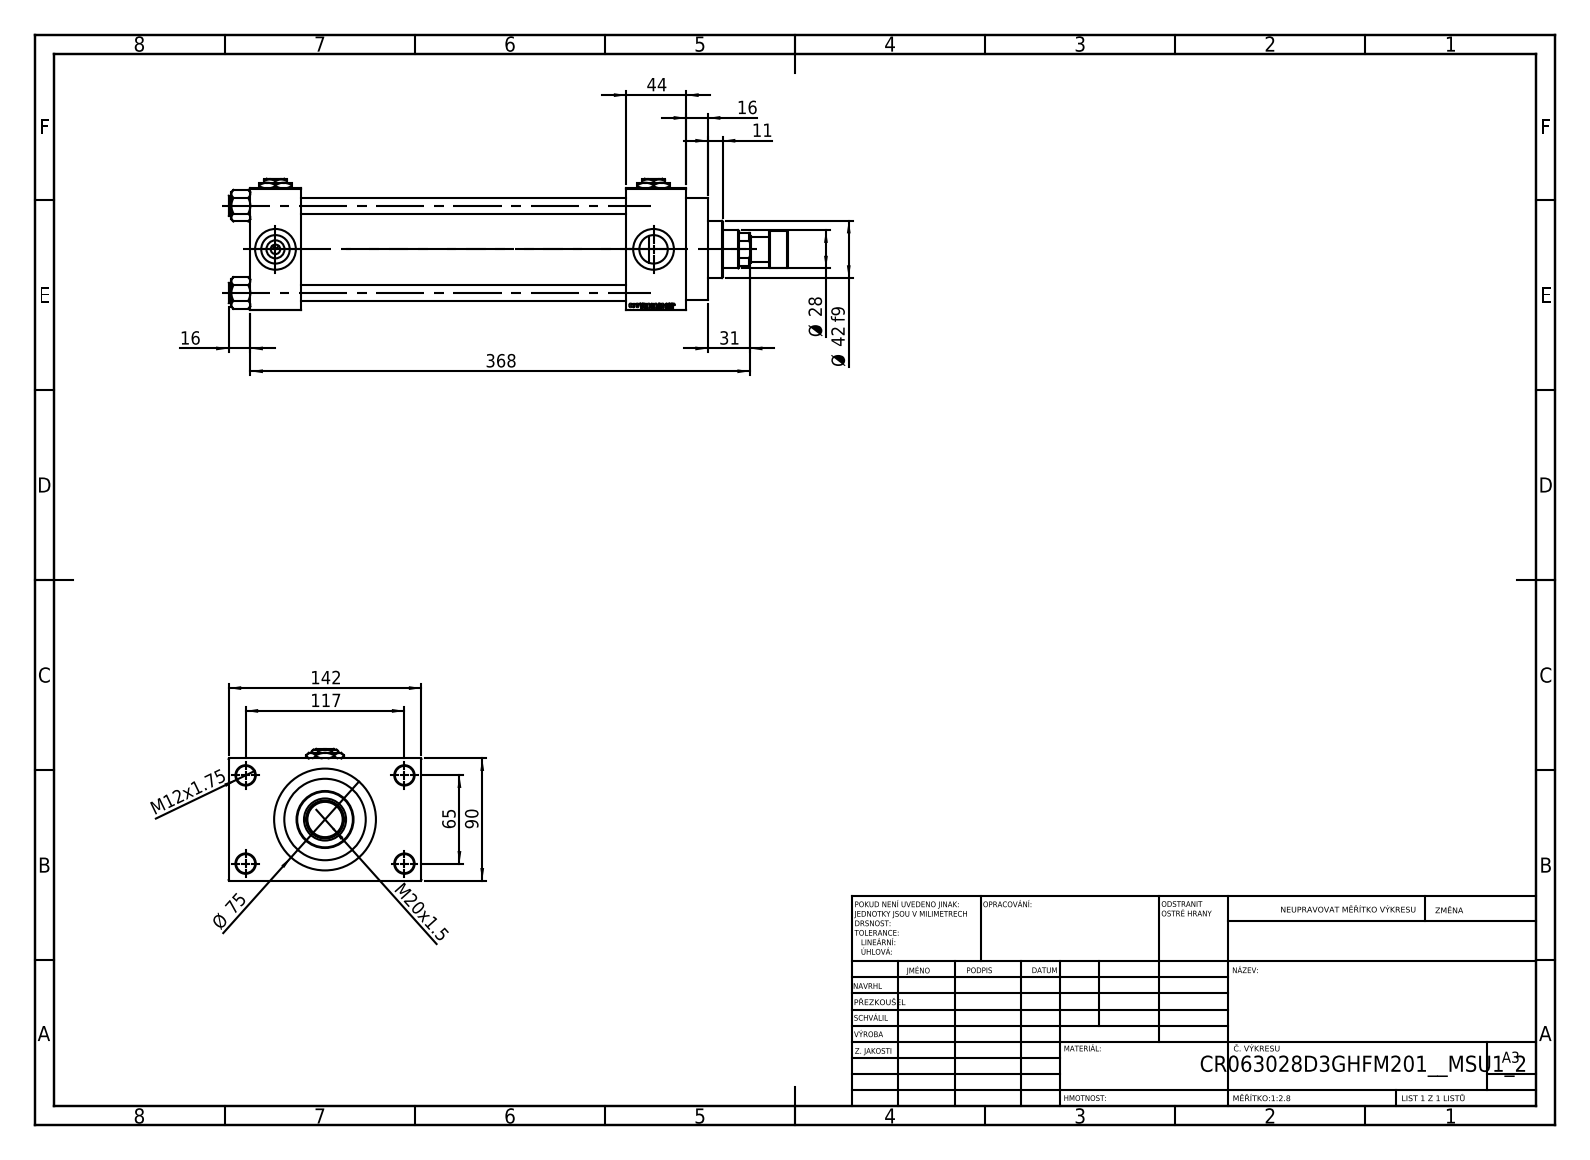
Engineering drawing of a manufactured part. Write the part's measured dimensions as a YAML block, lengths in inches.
part_name: "V215CR_ROD_END_F; Zatka_pro_OIL_PORT; V215CR_VCP_D; V215_VC_A (+3 more)"
step_written_by: "SolidWorks 2019 (CONFIG_CONTROL_DESIGN)"
units: inches
bodies: {solids: 14, faces: 1218, planar: 549, cylindrical: 103, other: 566}
overall_size: [16.22, 5.591, 3.819]
volume: 85.92
surface_area: 506
round_holes:
  - {diameter: 0.472, count: 4}
  - {diameter: 0.551, count: 4}
  - {diameter: 0.825, count: 4}
  - {diameter: 1.181, count: 4}
  - {diameter: 0.276, count: 3}
  - {diameter: 0.728, count: 1}
  - {diameter: 1.102, count: 1}
  - {diameter: 1.22, count: 1}
  - {diameter: 1.969, count: 1}
  - {diameter: 2.362, count: 1}
  - {diameter: 2.48, count: 1}
round_bosses_or_shafts:
  - {diameter: 0.591, count: 4}
  - {diameter: 2.953, count: 1}
  - {diameter: 2.717, count: 1}
  - {diameter: 1.654, count: 1}
  - {diameter: 1.063, count: 1}
  - {diameter: 0.709, count: 1}
face_to_face_distances: [3.543, 9.449, 1.457, 10.906, 11.181, 12.638, 1.732, 1.024, 4.567, 0.63]
hole_center_spacings: [1.037, 1.79, 2.531, 2.635, 2.748, 3.569, 4.383, 2.559]
